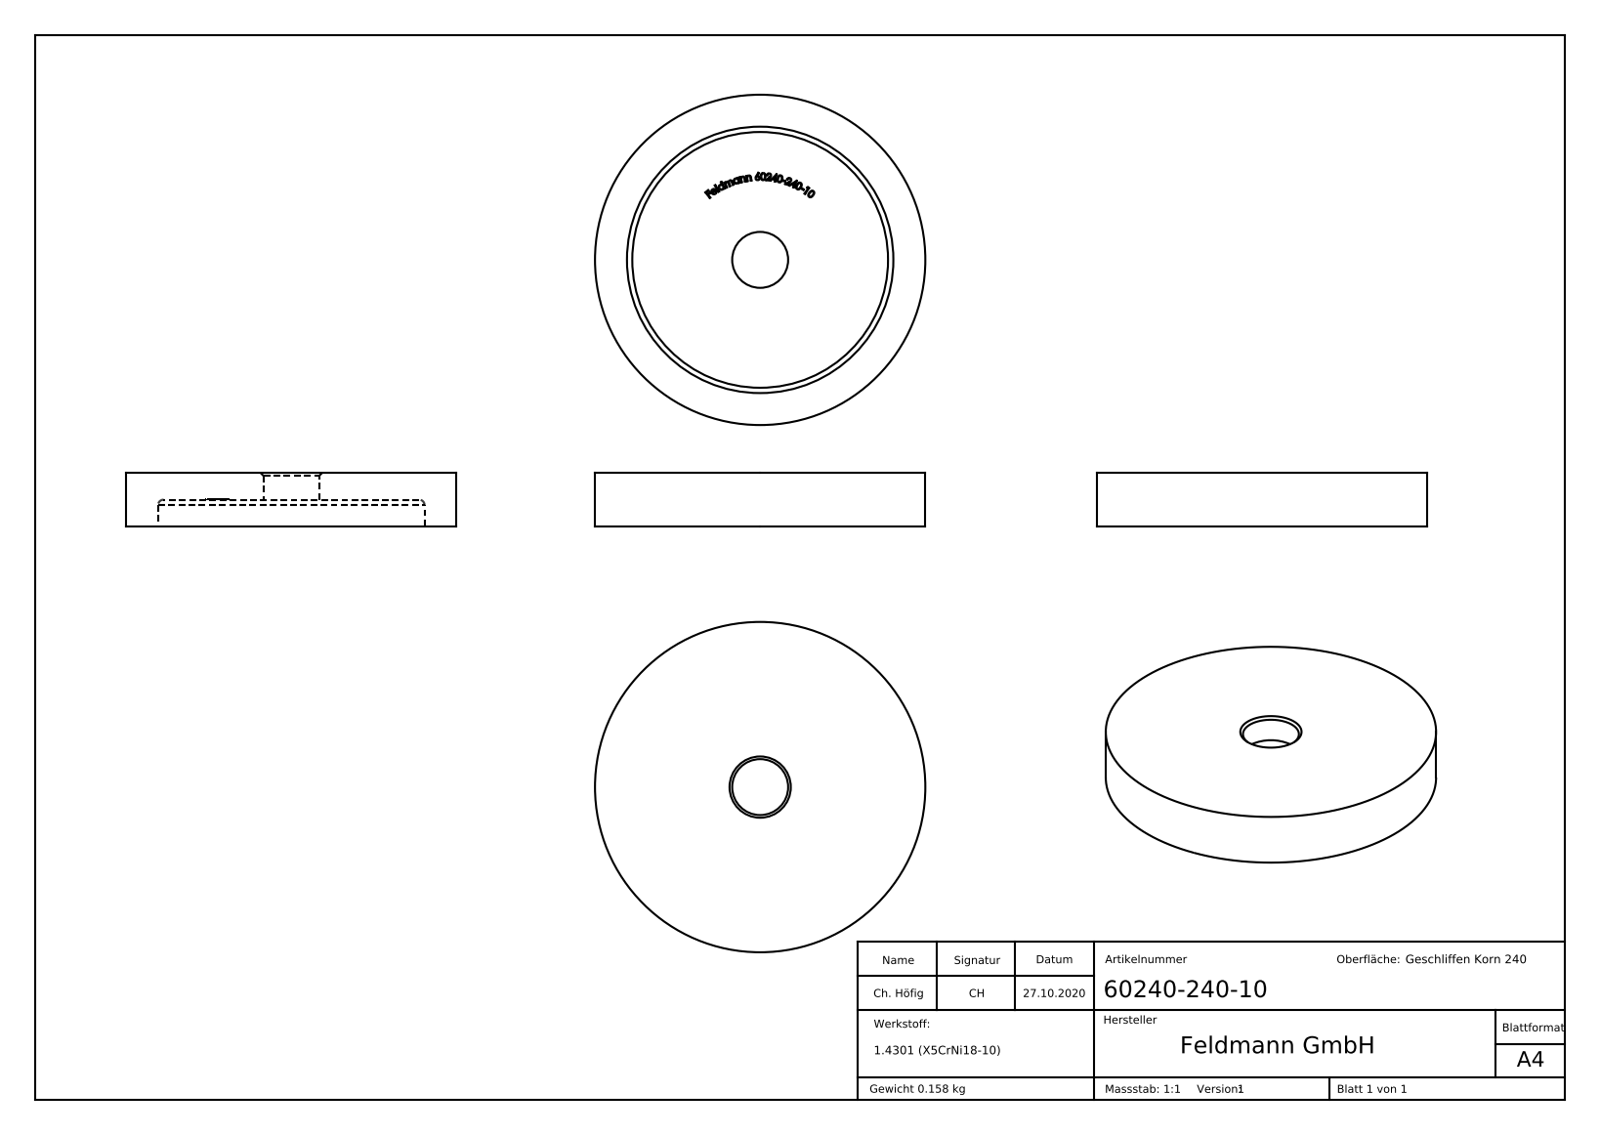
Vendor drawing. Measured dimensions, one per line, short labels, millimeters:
name: 60240-240-10
written by: SolidWorks 2018 (CONFIG_CONTROL_DESIGN)
unit: mm
bodies: 1 solid, 257 faces (142 planar, 6 cylindrical, 109 other)
size: 62 × 62 × 10
volume: 19 969 mm³; area: 8 697 mm²
holes: 1× ⌀10.5, 1× ⌀50
bosses: 1× ⌀62
face distances: 5, 10, 5.1, 4.9, 0.54, 1.33, 0.73, 1.46, 0.67, 0.41
